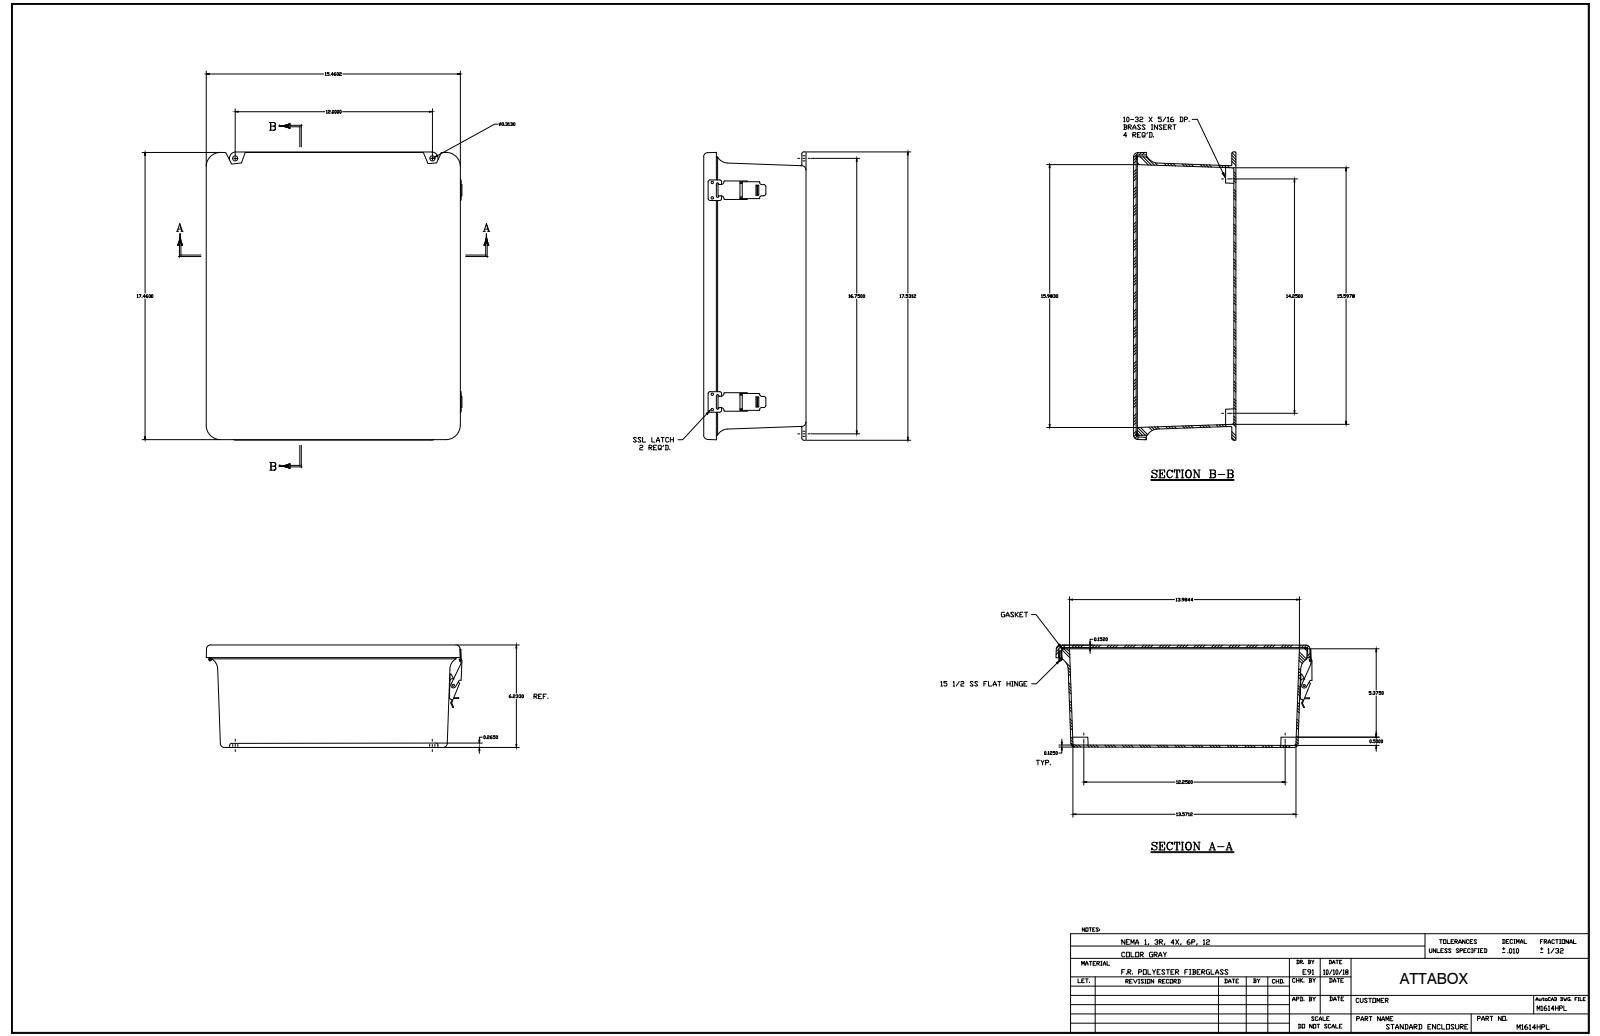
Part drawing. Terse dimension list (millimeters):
name: M1614HPL
written by: SolidWorks 2018 (AUTOMOTIVE_DESIGN)
unit: mm
bodies: 40 solids, 1060 faces (501 planar, 433 cylindrical, 126 other)
size: 445.3 × 396.1 × 158.1
volume: 2 370 000 mm³; area: 1 274 000 mm²
holes: 22× ⌀3.6, 18× ⌀2.6, 10× ⌀3.3, 4× ⌀3.3, 4× ⌀3.9, 4× ⌀4, 4× ⌀4.1, 4× ⌀5.5, 2× ⌀3.4, 2× ⌀9.5, 1× ⌀2.2
bosses: 13× ⌀3.2, 5× ⌀3.2, 4× ⌀6.9, 1× ⌀7.6, 1× ⌀4.3, 1× ⌀3.9, 1× ⌀3.4, 1× ⌀3
rounds: 20× R0.4, 20× R3.2, 16× R1.1, 12× R0.8, 8× R4.4, 8× R6.4, 6× R1.5, 5× R0.6
face distances: 3.2, 3.9, 158.1, 154.3, 155, 151.1, 3.2, 5.7, 1.9, 149.2
hole spacings: 95.3, 190.5, 285.8, 326.8, 6.4, 19.1, 327.4, 82.6
